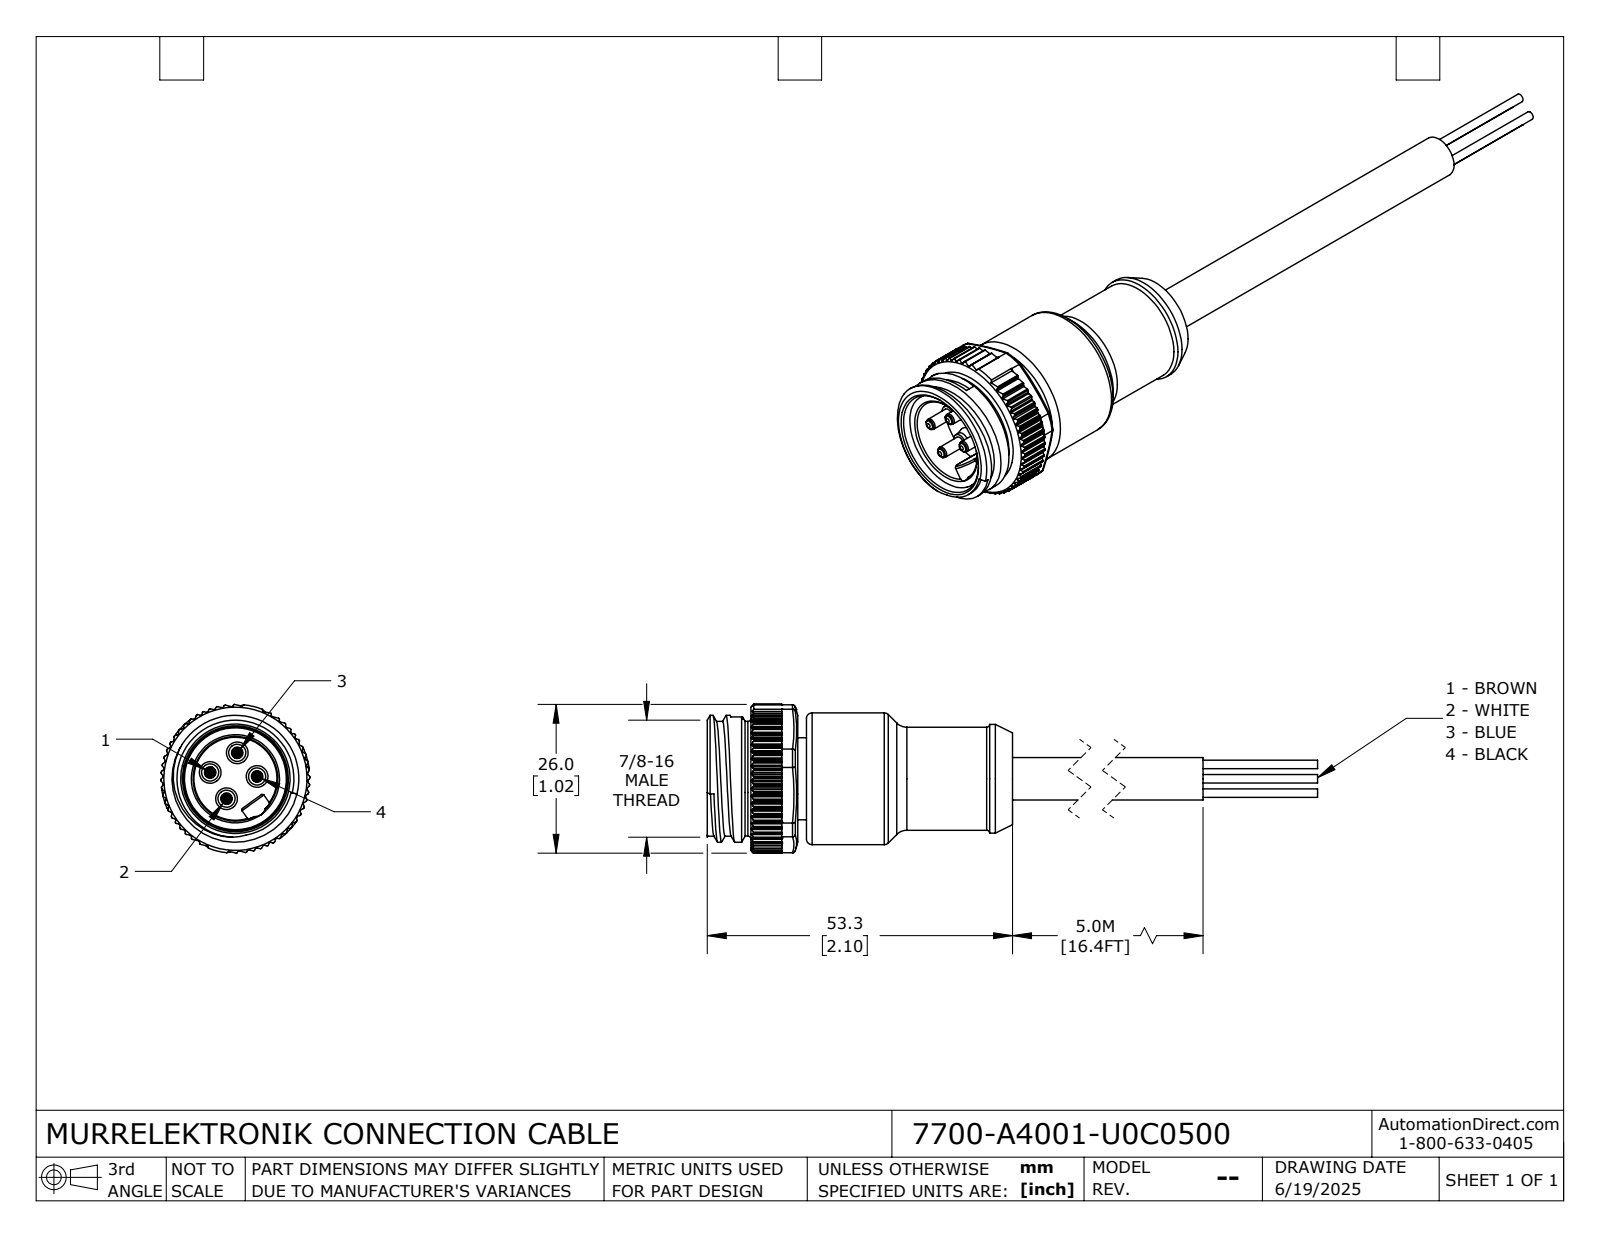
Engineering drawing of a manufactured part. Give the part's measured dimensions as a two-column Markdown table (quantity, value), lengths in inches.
| quantity | value |
| --- | --- |
| part name | 7700-A4001-U0C0500 |
| STEP written by | SolidWorks 2024 (CONFIG_CONTROL_DESIGN) |
| units | inches |
| bodies | 1 solid, 580 faces (236 planar, 266 cylindrical, 78 other) |
| overall size | 5.642 × 1.024 × 1.024 |
| volume | 1.227 in³ |
| surface area | 14.39 in² |
| round holes (diameter × count) | 0.614 × 1, 0.728 × 1 |
| round bosses / shafts (diameter × count) | 0.118 × 4, 0.079 × 4, 0.059 × 4, 0.906 × 1, 0.873 × 1, 0.789 × 1, 0.787 × 1, 0.748 × 1 |
| partial cylindrical surfaces (radius × count) | 0.008 × 126, 0.012 × 18, 0.004 × 4, 0.028 × 4, 0.093 × 1, 0.512 × 1 |
| main face-to-face distances | 0.059, 1.476, 1.417, 0.323, 0.382, 1.799, 0.035, 0.287, 0.346, 1.764 |
